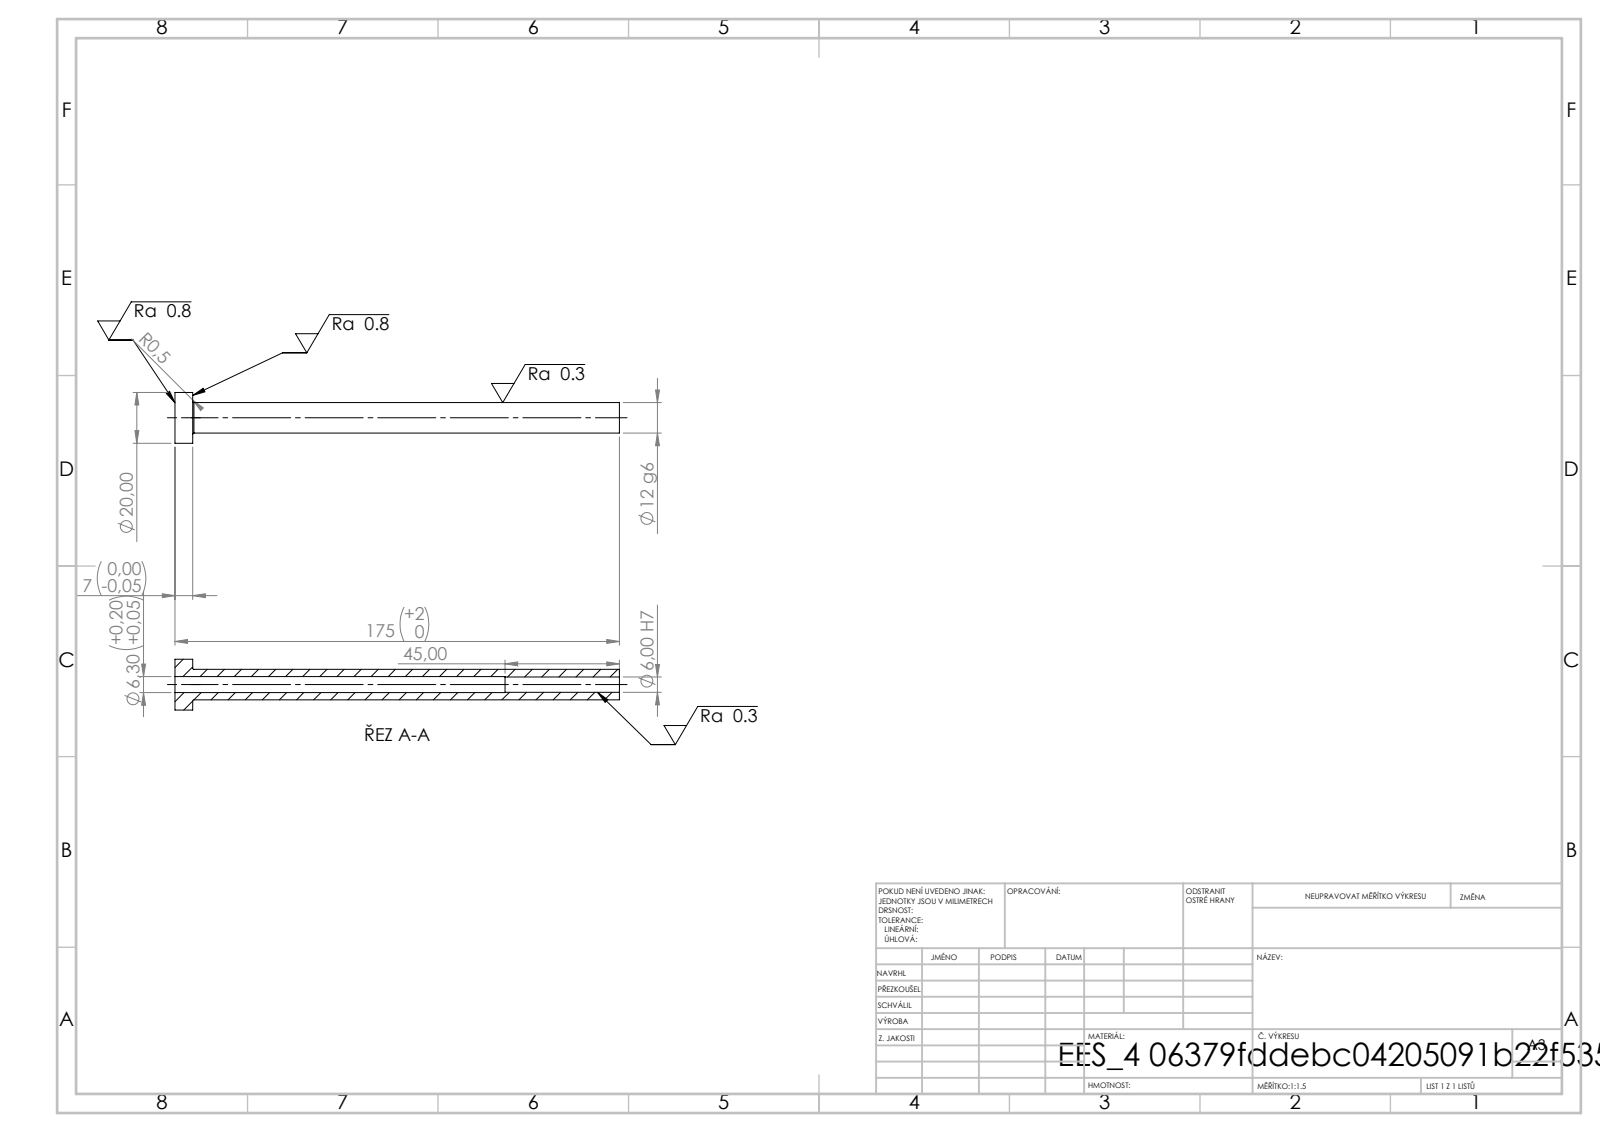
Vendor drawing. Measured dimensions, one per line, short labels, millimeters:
written by: SolidWorks 2019 (CONFIG_CONTROL_DESIGN)
unit: mm
bodies: 1 solid, 14 faces (4 planar, 8 cylindrical, 2 other)
size: 175 × 20 × 20
volume: 15 877 mm³; area: 10 758 mm²
holes: 1× ⌀6, 1× ⌀6.3
bosses: 1× ⌀20, 1× ⌀12
face distances: 7, 175, 168, 130, 123, 45
